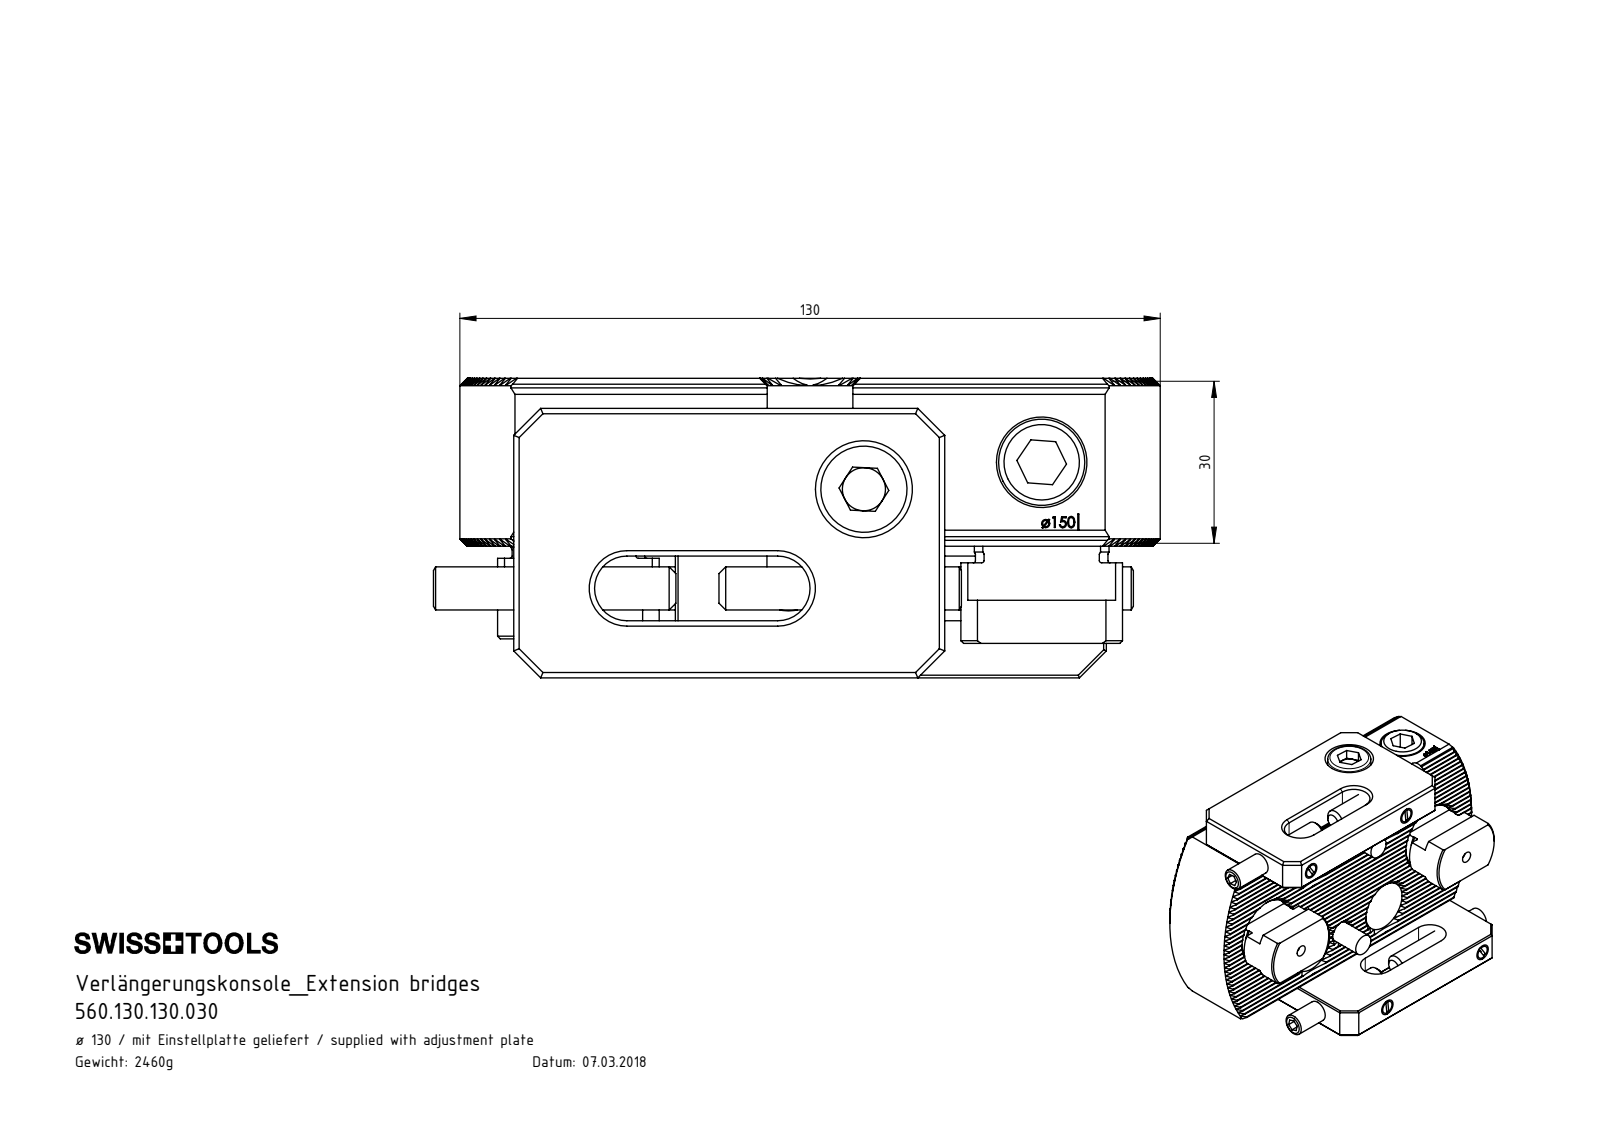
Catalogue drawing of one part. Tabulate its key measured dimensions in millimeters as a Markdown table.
| quantity | value |
| --- | --- |
| part name | VK1-ER7.001.012_mit kurzer Schraube; ISO 4766 - M6x12_ISO 4766 - M6 x 10; DIN 6912 - M10 x 12; ISO 4026 - M8 x 45 (+8 more) |
| STEP written by | SolidWorks 2017 (CONFIG_CONTROL_DESIGN) |
| units | millimeters |
| bodies | 27 solids, 1743 faces (968 planar, 467 cylindrical, 308 other) |
| overall size | 130 × 95 × 55.58 |
| volume | 319 917 mm³ |
| surface area | 101 240 mm² |
| round holes (diameter × count) | 5 × 4, 6 × 4, 6.8 × 4, 13 × 4, 19 × 4, 2 × 2, 8 × 2, 8.5 × 2, 10.5 × 2, 11 × 2, 14 × 2, 18 × 2 |
| round bosses / shafts (diameter × count) | 16 × 4, 6 × 4, 10 × 2, 8 × 2 |
| partial cylindrical surfaces (radius × count) | 0.14 × 66, 2 × 8, 6 × 4, 12.3 × 2, 15 × 2, 7.95 × 1, 65 × 1 |
| main face-to-face distances | 12, 82, 70, 0.5, 82.5, 11.5, 1.73, 70.5, 94, 71 |
| hole center spacings | 31.24, 65.15, 86, 2.05, 6.67, 7.9, 15, 17 |
